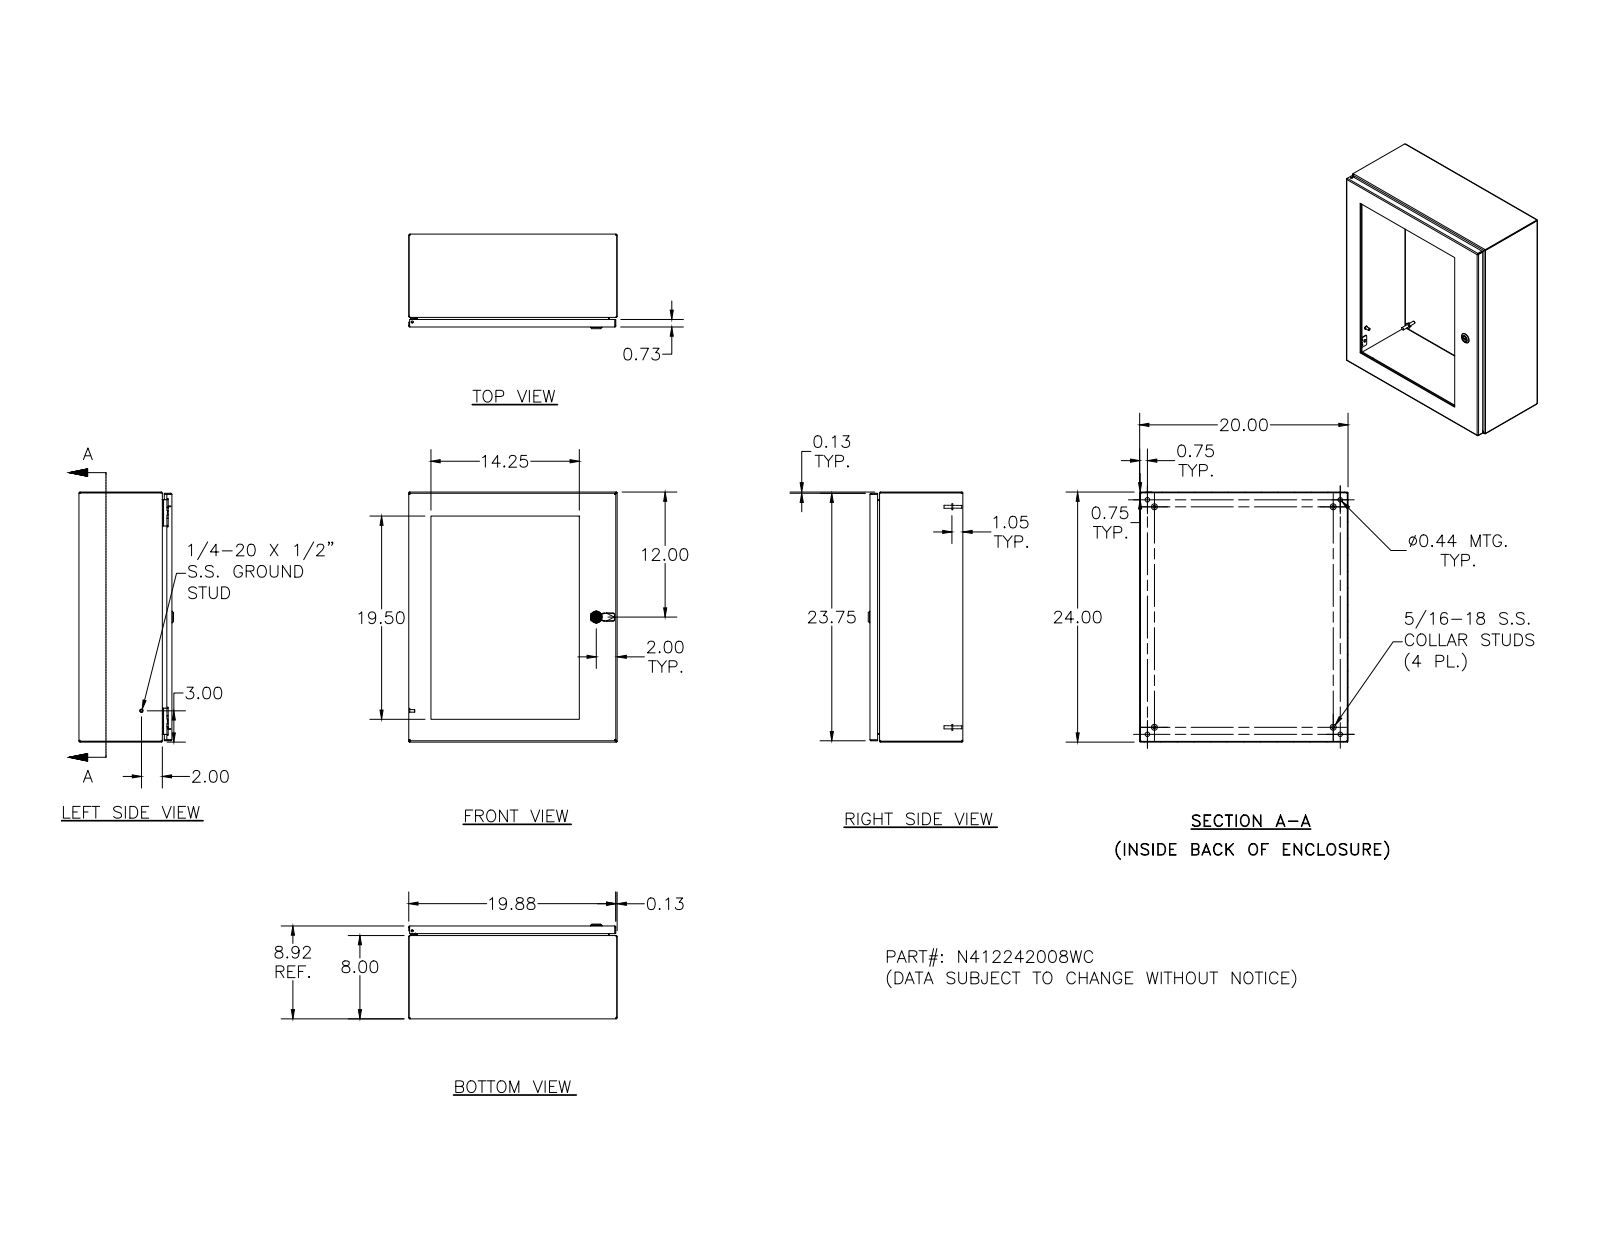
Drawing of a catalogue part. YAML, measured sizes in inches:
part_name: "N412242008WC"
step_written_by: "SolidWorks 2018 (AUTOMOTIVE_DESIGN)"
units: inches
bodies: {solids: 73, faces: 2083, planar: 775, cylindrical: 625, other: 683}
overall_size: [24, 20, 9.075]
volume: 199.9
surface_area: 3972
round_holes:
  - {diameter: 0.156, count: 20}
  - {diameter: 0.281, count: 18}
  - {diameter: 0.188, count: 5}
  - {diameter: 0.093, count: 4}
  - {diameter: 0.152, count: 4}
  - {diameter: 0.167, count: 4}
  - {diameter: 0.172, count: 4}
  - {diameter: 0.437, count: 4}
  - {diameter: 0.187, count: 1}
  - {diameter: 0.197, count: 1}
  - {diameter: 0.315, count: 1}
  - {diameter: 0.394, count: 1}
round_bosses_or_shafts:
  - {diameter: 0.337, count: 18}
  - {diameter: 0.19, count: 18}
  - {diameter: 0.25, count: 10}
  - {diameter: 0.563, count: 4}
  - {diameter: 0.36, count: 4}
  - {diameter: 0.32, count: 4}
  - {diameter: 0.3, count: 4}
  - {diameter: 0.275, count: 4}
partial_cylinders:
  - {radius: 0.031, count: 34}
  - {radius: 0.012, count: 30}
  - {radius: 0.05, count: 26}
  - {radius: 0.105, count: 24}
  - {radius: 0.016, count: 18}
  - {radius: 0.125, count: 16}
  - {radius: 0.02, count: 13}
  - {radius: 0.032, count: 8}
face_to_face_distances: [0.074, 8.843, 8.769, 19.926, 0.25, 8.593, 8.519, 23.926, 19.852, 20]
hole_center_spacings: [4, 8, 16.008, 12, 17.443, 20, 21.132, 15.5]
